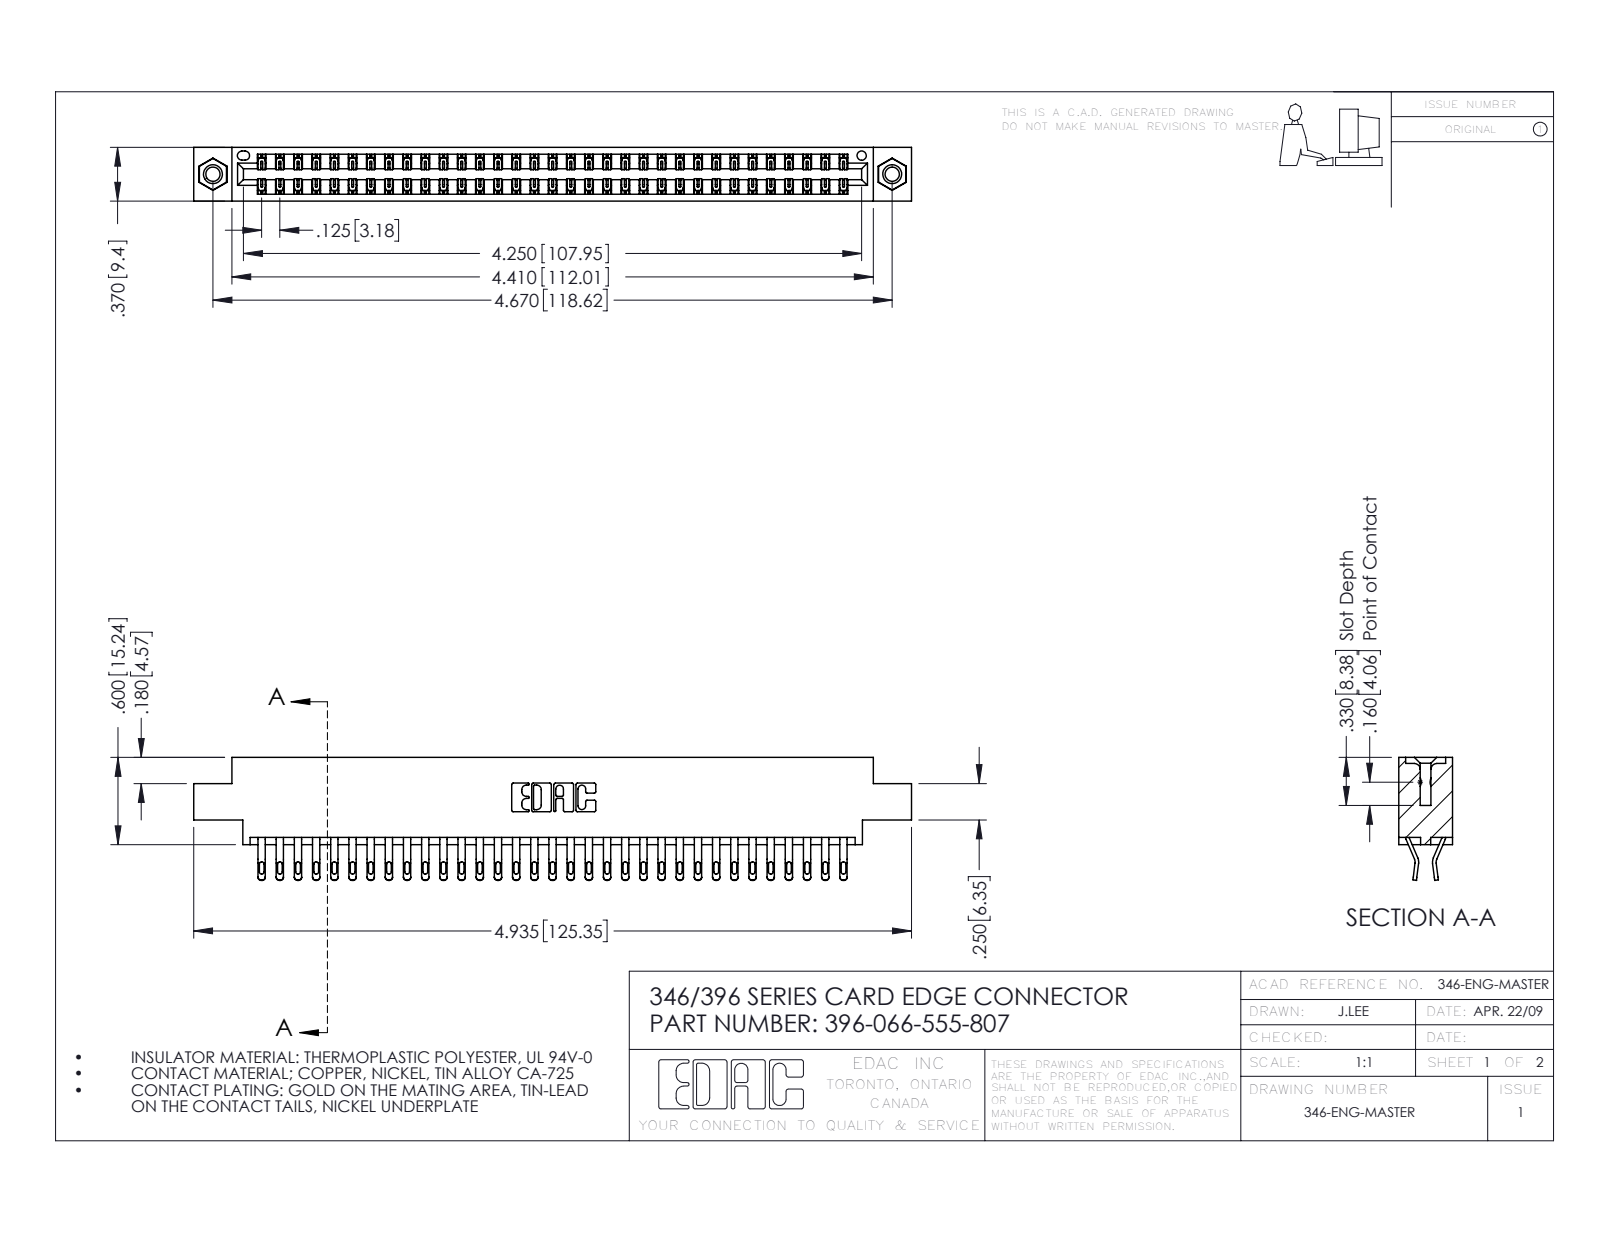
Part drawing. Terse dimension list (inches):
name: 396-066-555-807; 346 Part_0.170 Offset - 0.156 Dia-TI; 345-292-001_555 Tail; 345-250-001_345-250-005-103
written by: SolidWorks 2016 (CONFIG_CONTROL_DESIGN)
unit: in
bodies: 69 solids, 4014 faces (2290 planar, 1708 cylindrical, 16 other)
size: 4.935 × 0.845 × 0.37
volume: 0.743 in³; area: 27.11 in²
holes: 2× ⌀0.098, 2× ⌀0.125, 2× ⌀0.156, 1× ⌀0.064
bosses: 2× ⌀0.155
rounds: 132× R0.016, 132× R0.02, 99× R0.006, 22× R0.01, 6× R0.007, 6× R0.031, 3× R0.026, 2× R0.01
face distances: 0.048, 0.322, 0.37, 0.25, 0.025, 0.072, 0.298, 0.275, 0.222, 0.148
hole spacings: 0.246, 4.462, 4.67
